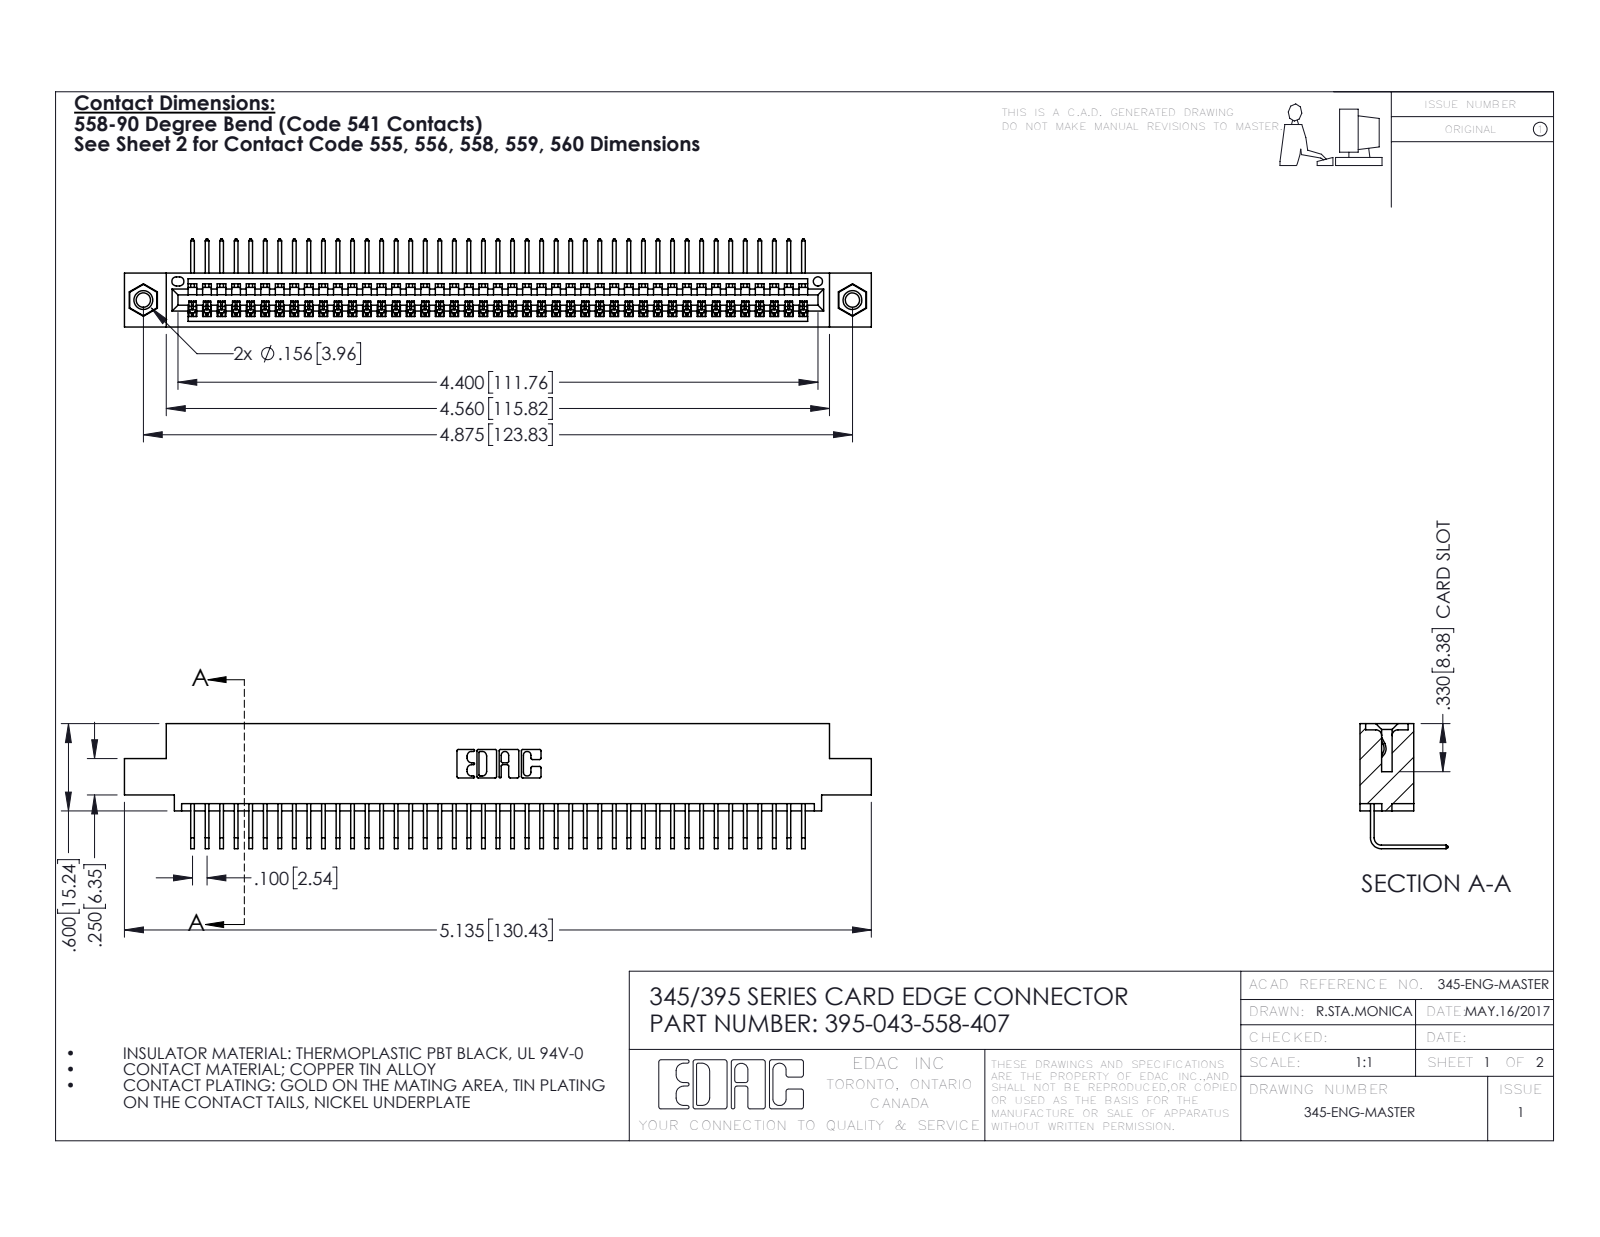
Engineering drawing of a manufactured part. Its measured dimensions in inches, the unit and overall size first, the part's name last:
Units: inches
Overall size (bounding box): 5.135 × 0.859 × 0.605
Round holes (diameter × count): ⌀0.098 ×2, ⌀0.125 ×2, ⌀0.156 ×2, ⌀0.064 ×1
Round bosses / shafts (diameter × count): ⌀0.155 ×2
Partial cylindrical surfaces — rounded edges, fillets, slot ends (radius × count): R0.006 ×86, R0.01 ×22, R0.007 ×6, R0.031 ×6, R0.026 ×3, R0.031 ×2, R0.04 ×2, R0.014 ×1
Main face-to-face distances: 0.072, 0.298, 0.37, 0.2, 0.098, 0.272, 0.025, 0.225, 0.149, 0.072
Hole centre spacings: 0.27, 4.639, 4.875
Volume: 0.76 in³ · Surface area: 27.15 in²
Bodies: 46 solids, 2770 faces (1922 planar, 832 cylindrical, 16 other)
Part name (STEP PRODUCT): 345 Part_0.110 Offset - 0.156 Dia-TI; 345-250-001_345-250-005-103; 345-292-001_558 Tail - 2; 395-043-558-407
STEP written by: SolidWorks 2016 (CONFIG_CONTROL_DESIGN)
